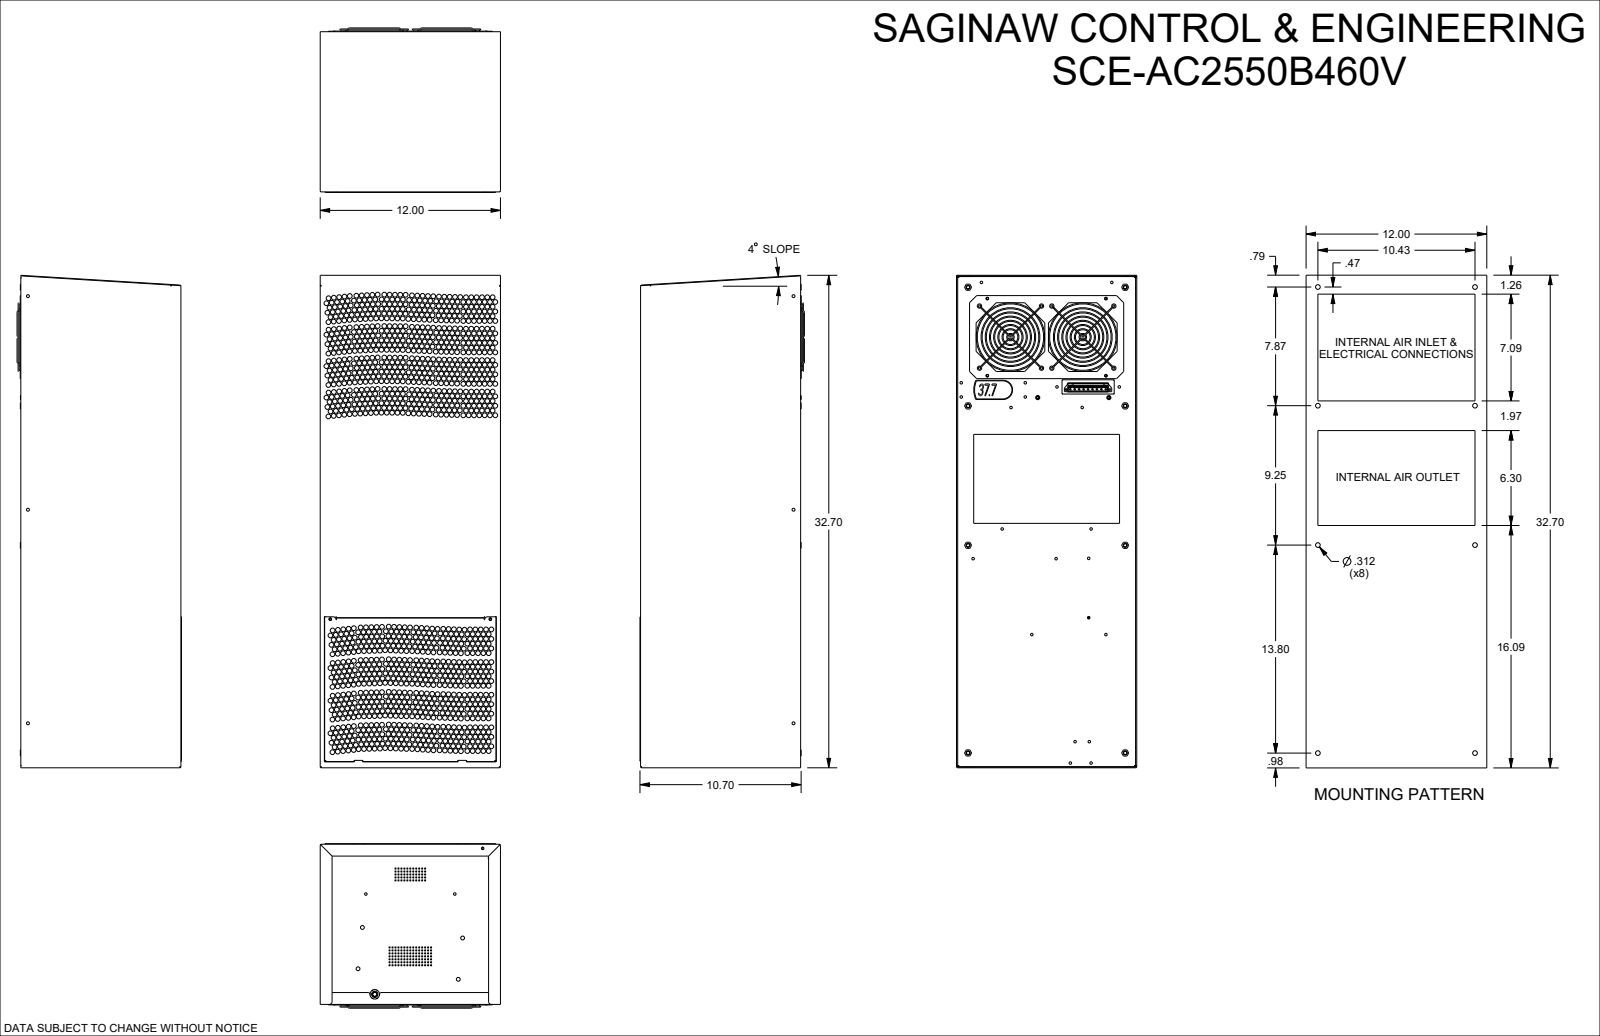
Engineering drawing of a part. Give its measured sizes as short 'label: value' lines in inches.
name: SCE-AC2550B120V-2
written by: SolidWorks 2021 (AUTOMOTIVE_DESIGN)
unit: in
bodies: 54 solids, 2262 faces (1397 planar, 621 cylindrical, 244 other)
size: 32.682 × 11.969 × 10.921
volume: 118.5 in³; area: 4 854 in²
holes: 160× ⌀0.079, 70× ⌀0.169, 57× ⌀0.315, 9× ⌀0.165, 8× ⌀0.142, 8× ⌀0.217, 8× ⌀0.264, 4× ⌀0.126, 4× ⌀0.256, 3× ⌀0.197, 2× ⌀0.106, 2× ⌀0.177
bosses: 11× ⌀0.276, 11× ⌀0.236, 9× ⌀0.11, 8× ⌀0.071, 1× ⌀0.474, 1× ⌀0.394
rounds: 25× R0.079, 21× R0.039, 9× R0.118, 6× R0.02, 6× R0.059, 2× R0.049, 2× R0.051, 1× R0.315
face distances: 0.039, 0.079, 11.85, 11.89, 11.811, 0.118, 11.929, 10.591, 11.772, 10.63
hole spacings: 0.197, 0.278, 0.44, 0.394, 0.622, 0.591, 0.812, 0.787
